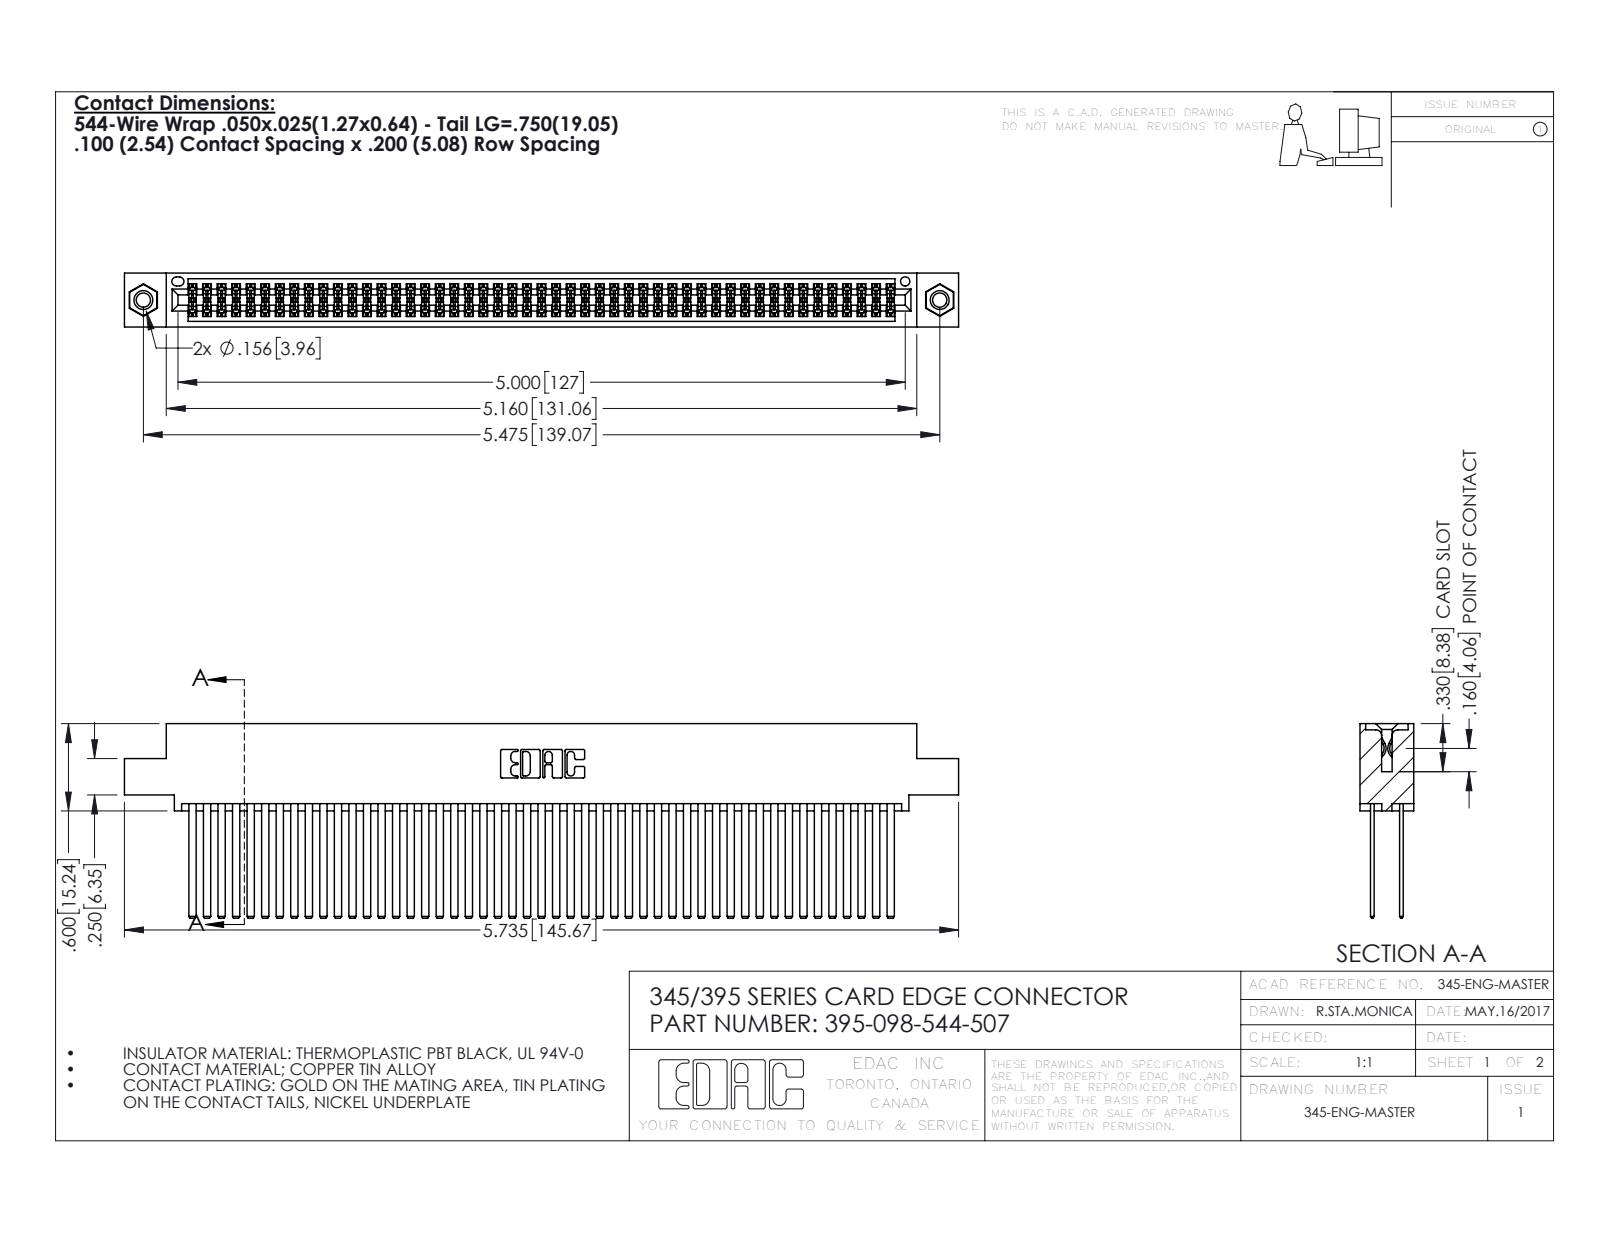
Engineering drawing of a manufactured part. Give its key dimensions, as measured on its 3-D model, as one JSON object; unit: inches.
{"part_name": "345 Part_0.110 Offset - 0.156 Dia-TI; 345-250-001_345-250-005-103; 395-098-544-507; 345-292-001_345-293-144", "step_written_by": "SolidWorks 2016 (CONFIG_CONTROL_DESIGN)", "units": "inches", "bodies": {"solids": 101, "faces": 4502, "planar": 2958, "cylindrical": 1528, "other": 16}, "overall_size": [5.735, 1.337, 0.37], "volume_in3": 0.946, "surface_area_in2": 42.16, "round_holes": [[0.098, 2], [0.125, 2], [0.156, 2], [0.064, 1]], "round_bosses_or_shafts": [[0.155, 2]], "partial_cylinders_radius": [[0.006, 147], [0.01, 22], [0.007, 6], [0.031, 6], [0.026, 3], [0.014, 2], [0.019, 2], [0.022, 2]], "face_to_face_distances": [0.2, 0.025, 0.072, 0.098, 0.272, 0.298, 0.225, 0.175, 0.37, 0.05], "hole_center_spacings": [0.27, 5.239, 5.475]}
